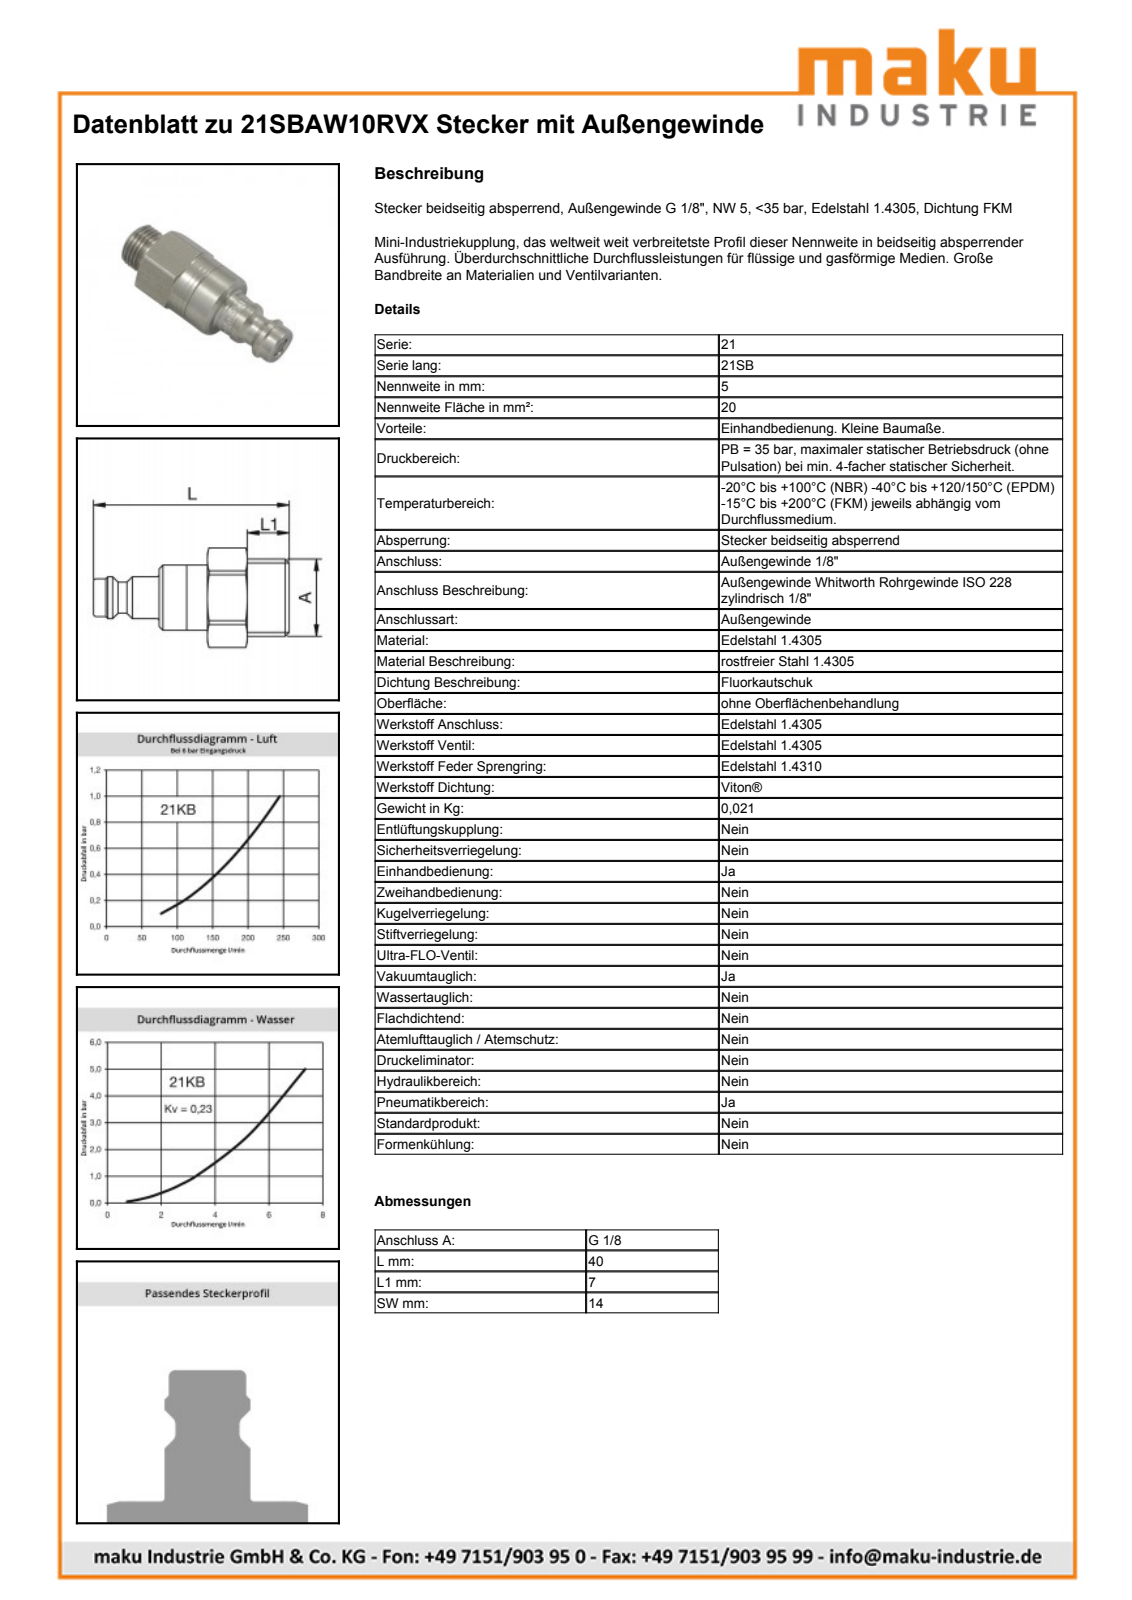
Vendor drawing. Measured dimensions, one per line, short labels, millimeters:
name: D109503
written by: Autodesk Inventor 2013 (AUTOMOTIVE_DESIGN)
unit: mm
bodies: 1 solid, 56 faces (13 planar, 16 cylindrical, 27 other)
size: 40 × 15.67 × 15.03
volume: 4 240 mm³; area: 2 032 mm²
holes: 1× ⌀12
bosses: 1× ⌀14, 1× ⌀11.09, 1× ⌀9.73, 1× ⌀9, 1× ⌀8.1, 1× ⌀6.7
rounds: 1× R7.9
face distances: 14, 7, 18.9, 25.9, 14.1, 33, 40, 20, 25, 10.9
